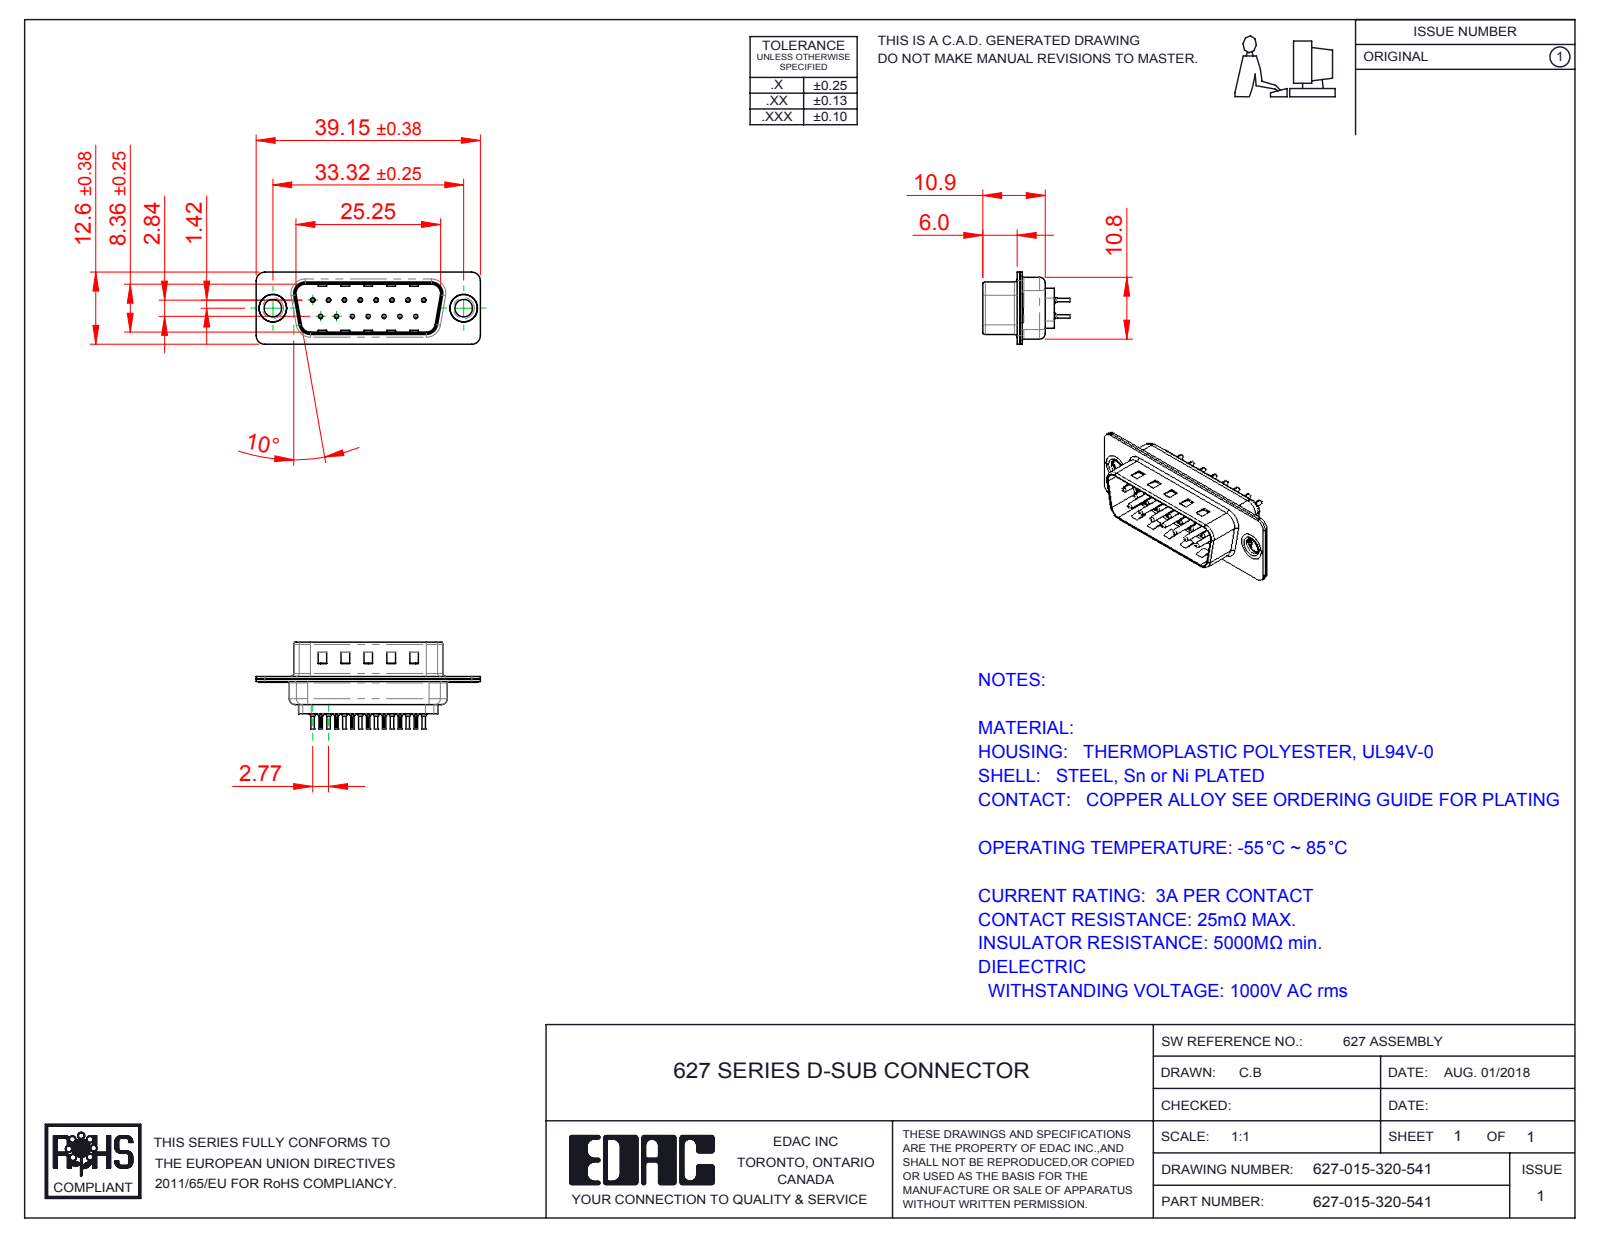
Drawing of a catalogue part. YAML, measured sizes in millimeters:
part_name: "627 Thru Hole Rivet; 627 Contact Row 1_20L; 627 Shell Front_15 Contacts; 627 Shell Rear_15 Contacts (+3 more)"
step_written_by: "SolidWorks 2016 (CONFIG_CONTROL_DESIGN)"
units: millimeters
bodies: {solids: 20, faces: 1784, planar: 499, cylindrical: 672, other: 613}
overall_size: [39.15, 15.2, 12.6]
volume: 1745
surface_area: 5157
round_holes:
  - {diameter: 0.2, count: 15}
  - {diameter: 0.35, count: 15}
  - {diameter: 1.1, count: 15}
  - {diameter: 1.6, count: 15}
  - {diameter: 3.05, count: 2}
  - {diameter: 4, count: 2}
  - {diameter: 4.8, count: 2}
round_bosses_or_shafts:
  - {diameter: 2, count: 15}
  - {diameter: 1.5, count: 15}
  - {diameter: 0.75, count: 15}
  - {diameter: 0.6, count: 15}
  - {diameter: 5, count: 2}
  - {diameter: 4.9, count: 2}
  - {diameter: 3.55, count: 2}
partial_cylinders:
  - {radius: 0.1, count: 30}
  - {radius: 1.5, count: 16}
  - {radius: 2, count: 12}
  - {radius: 0.5, count: 8}
  - {radius: 1.6, count: 8}
  - {radius: 0.25, count: 4}
  - {radius: 0.6, count: 4}
  - {radius: 0.65, count: 4}
face_to_face_distances: [0.4, 0.45, 0.9, 0.82, 9.58, 8.76, 1.5, 1.4, 0.5, 6.5]
hole_center_spacings: [3.16, 2.77, 5.54, 8.31, 11.08, 5.03, 5.04, 7.48]
